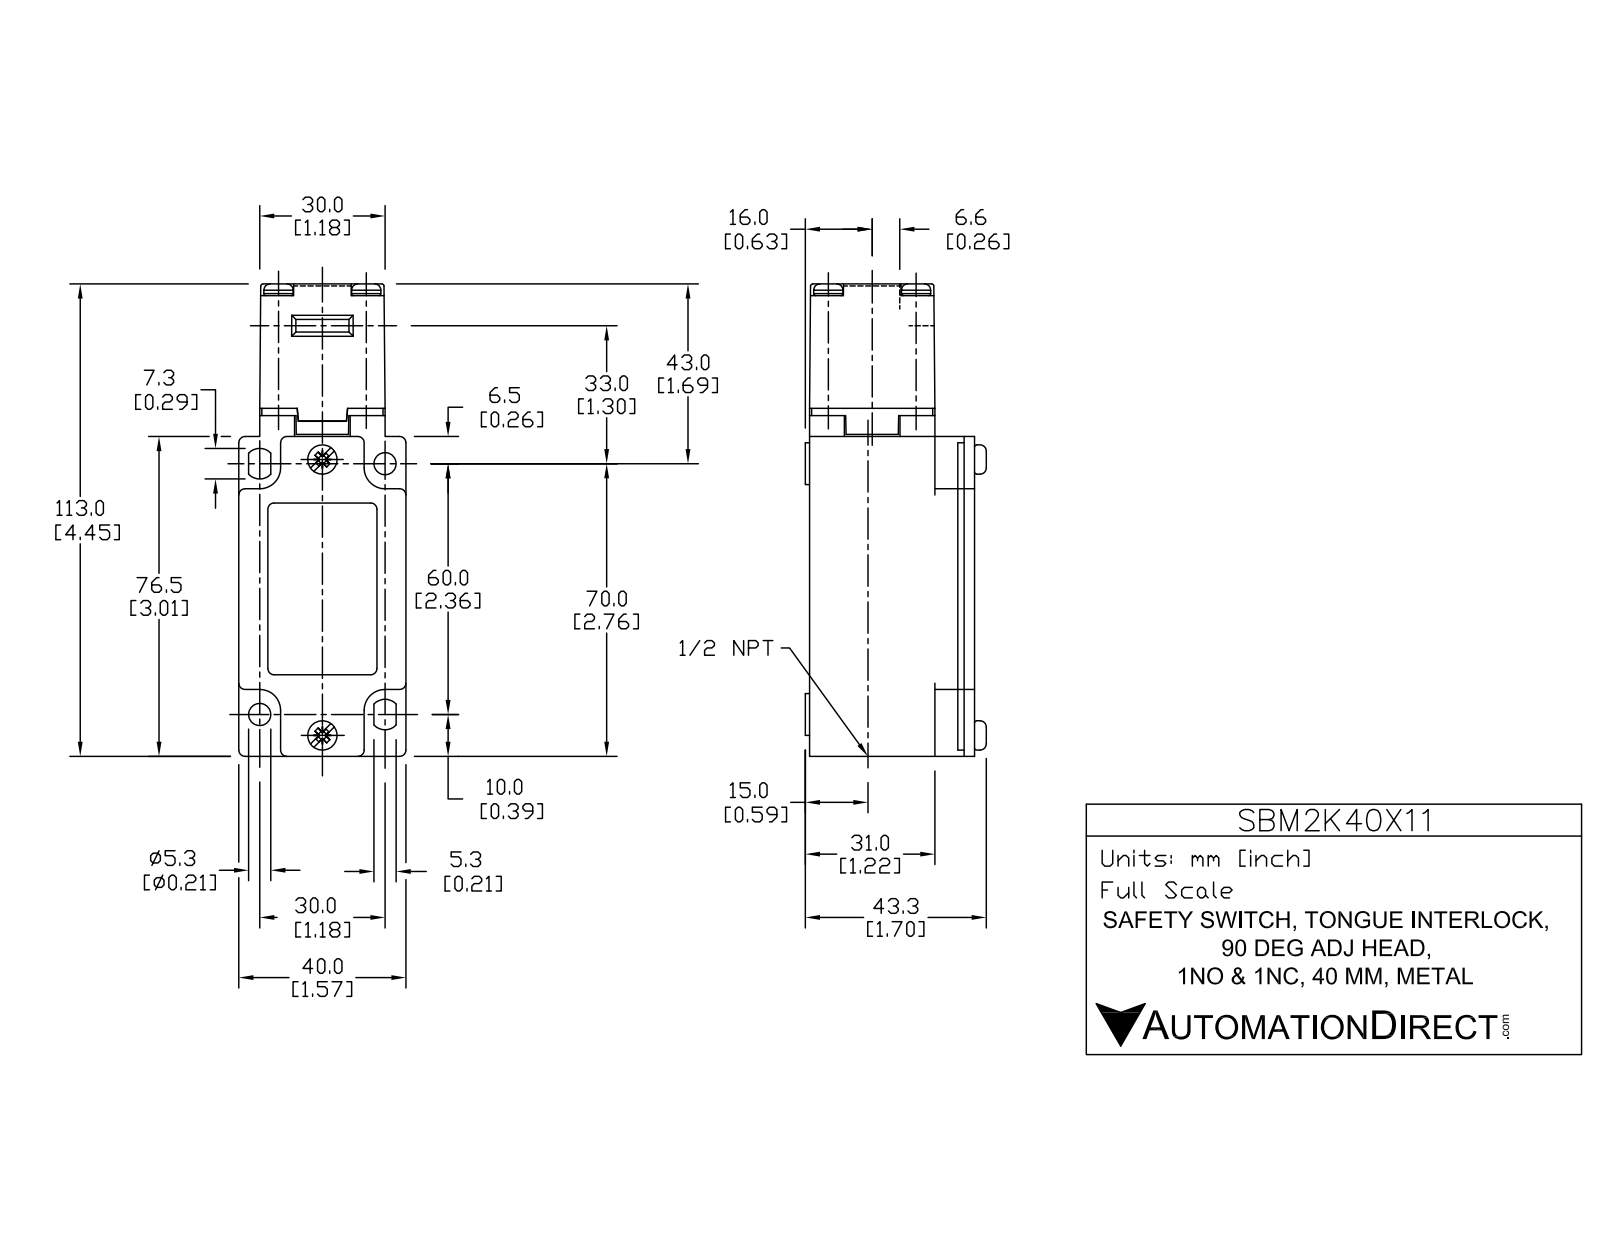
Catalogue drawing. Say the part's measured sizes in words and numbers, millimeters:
The part is named "SBM2K40X11". Its 3-D file was written by "SolidWorks 2017 (AUTOMOTIVE_DESIGN)". It is 2 solids with 183 faces: 97 planar, 72 cylindrical and 14 other. Overall it measures 113 by 43.3 by 40 millimeters. Its volume is 139 400 cubic millimeters and its surface area 26 420 square millimeters. Round holes: 2 of diameter 5.2, 2 of diameter 7, 1 of diameter 17, 1 of diameter 19. Round bosses or shafts: 4 of diameter 10, 4 of diameter 7. Partial cylindrical surfaces (rounded edges, fillets, slot ends): 16 of radius 1.5, 4 of radius 0.5, 4 of radius 5, 2 of radius 3.3, 1 of radius 11.5, 1 of radius 12. The main face-to-face distances are 30, 5, 40, 39.5, 35, 9.5, 76.5, 3, 0.5, 25. The hole center spacings are 14.1, 21, 67.1.
